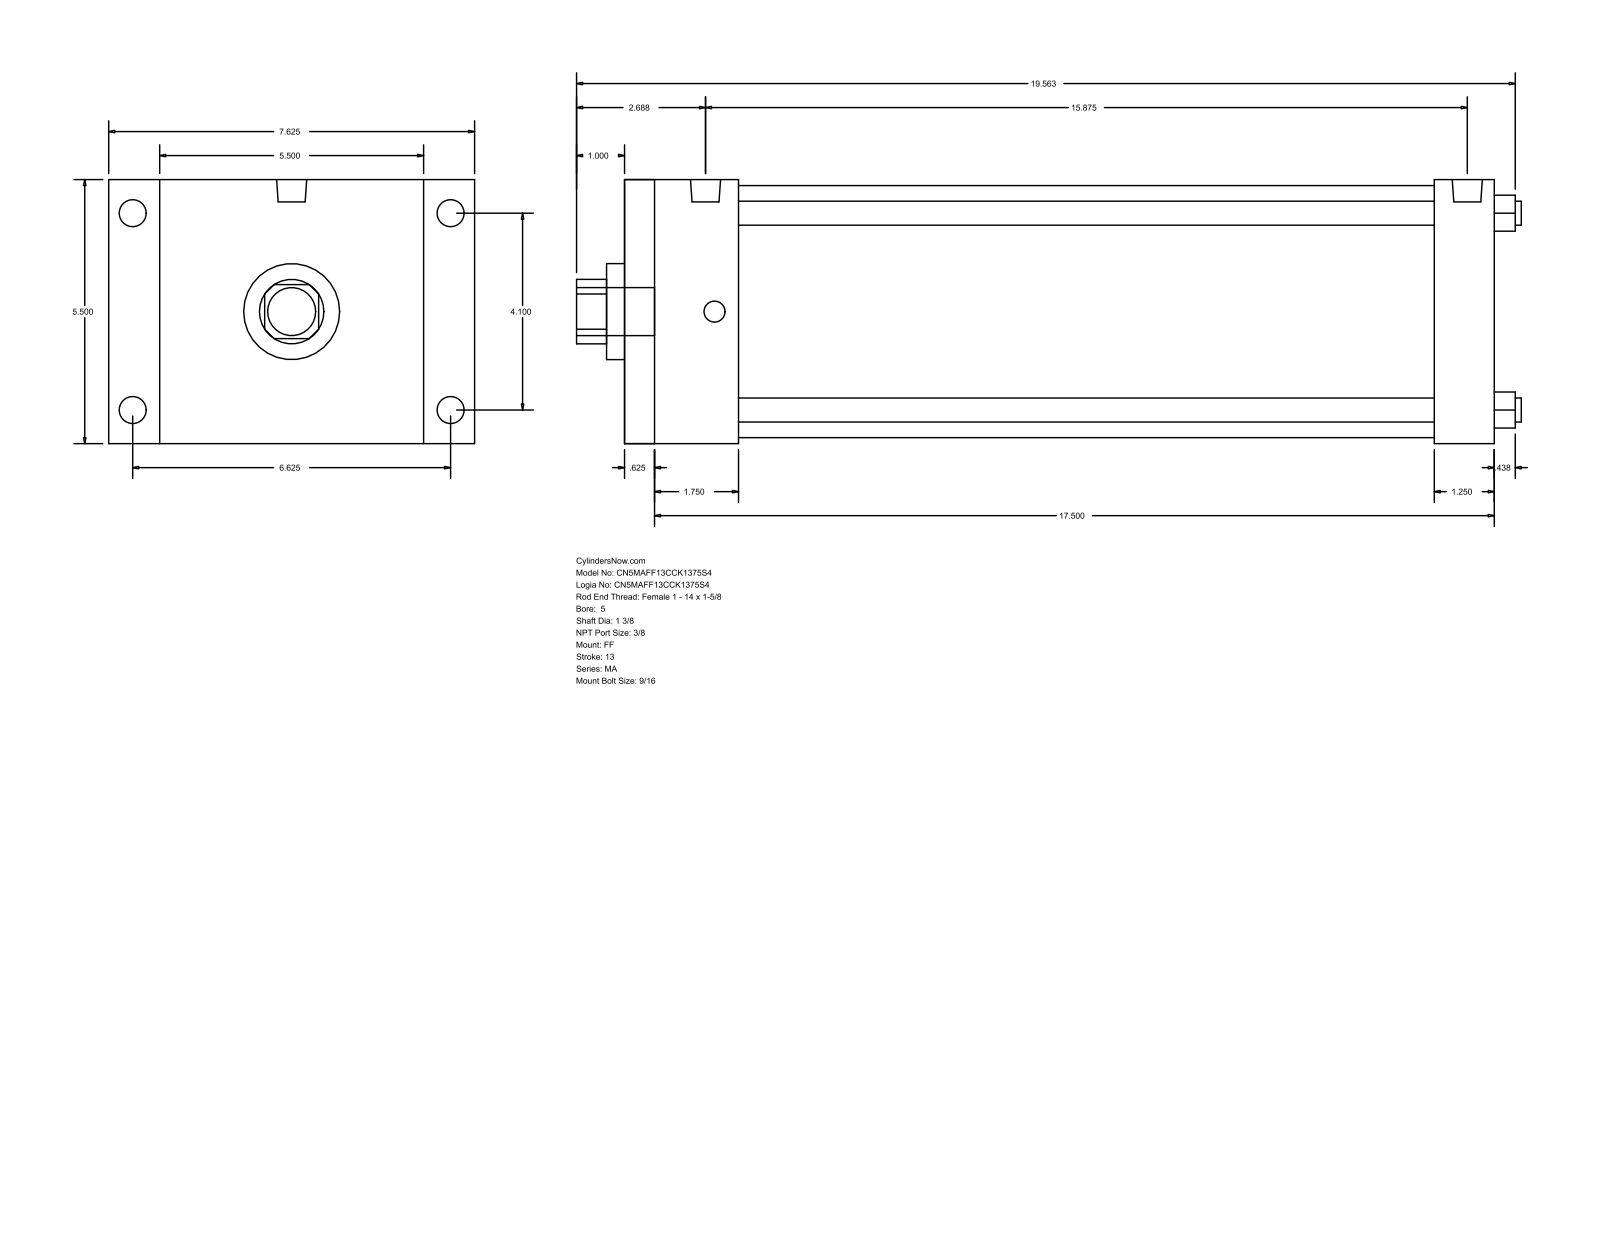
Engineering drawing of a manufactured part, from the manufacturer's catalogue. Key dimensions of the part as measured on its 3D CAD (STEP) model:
Part name (STEP PRODUCT): MA_FF__0500_1.375
STEP written by: GSSL Pune (CONFIG_CONTROL_DESIGN)
Units: millimetres
Bodies: 0 solids, 92 faces (64 planar, 28 cylindrical, 0 other)
Overall size (bounding box): 500.06 × 193.68 × 139.7
Round holes (diameter × count): ⌀12.7 ×4, ⌀34.92 ×1, ⌀50.8 ×1, ⌀133.35 ×1
Round bosses / shafts (diameter × count): ⌀14.29 ×4, ⌀11.11 ×4, ⌀15.93 ×2, ⌀25.4 ×1
Partial cylindrical surfaces — rounded edges, fillets, slot ends (radius × count): R17.06 ×1
Main face-to-face distances: 139.7, 460.37, 15.87, 444.5, 428.62, 412.75, 31.75, 60.32, 44.45, 368.3
Hole centre spacings: 73.64, 104.14, 147.28
